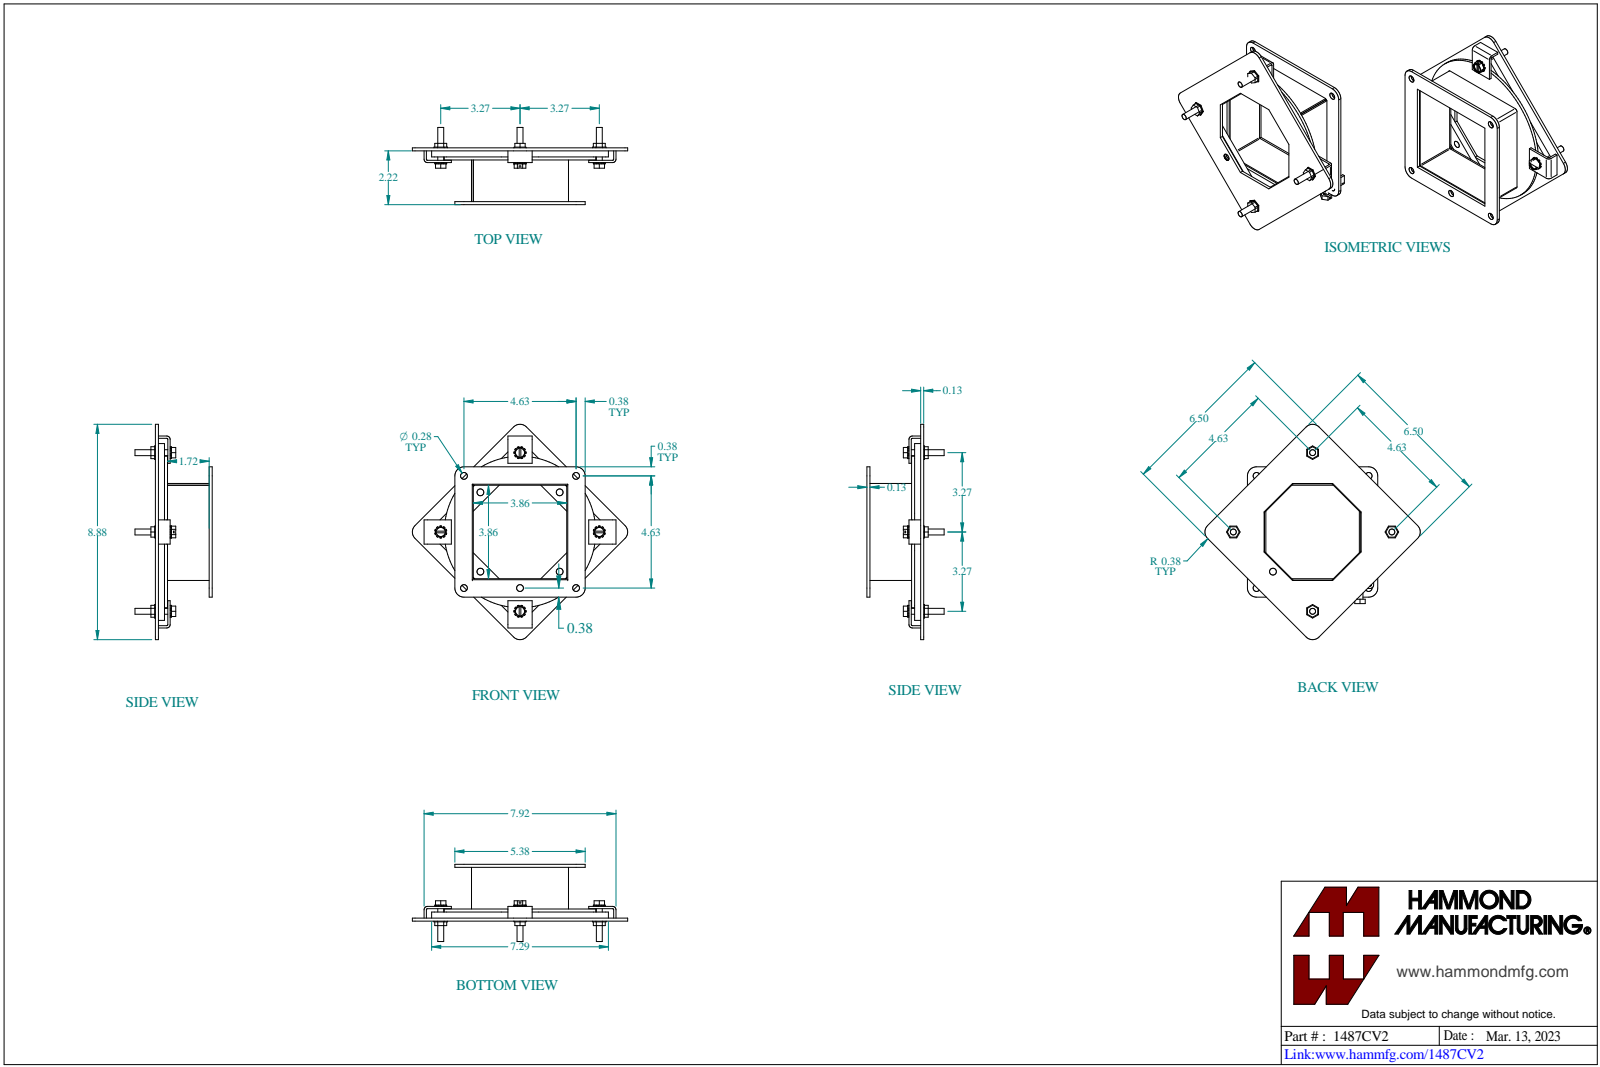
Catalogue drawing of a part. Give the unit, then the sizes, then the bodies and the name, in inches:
Units: inches
Overall size (bounding box): 8.882 × 8.882 × 3.309
Round holes (diameter × count): ⌀0.281 ×16, ⌀0.196 ×4, ⌀0.258 ×4, ⌀0.312 ×4, ⌀0.375 ×4, ⌀0.375 ×1
Round bosses / shafts (diameter × count): ⌀0.244 ×4, ⌀6.25 ×1
Partial cylindrical surfaces — rounded edges, fillets, slot ends (radius × count): R0.25 ×12, R0.375 ×12, R0.048 ×4, R0.062 ×4, R0.143 ×4, R0.036 ×3, R0.108 ×3
Main face-to-face distances: 0.125, 0.25, 2.218, 1.968, 0.125, 0.375, 2.093, 2.343, 0.072, 3.928
Hole centre spacings: 5.171, 2.313, 4.005, 2.312, 3.27, 4.625, 4.006, 4.625
Volume: 14.77 in³ · Surface area: 275.8 in²
Bodies: 22 solids, 532 faces (342 planar, 180 cylindrical, 10 other)
Part name (STEP PRODUCT): 1487CV2
STEP written by: SolidWorks 2023 (CONFIG_CONTROL_DESIGN)
